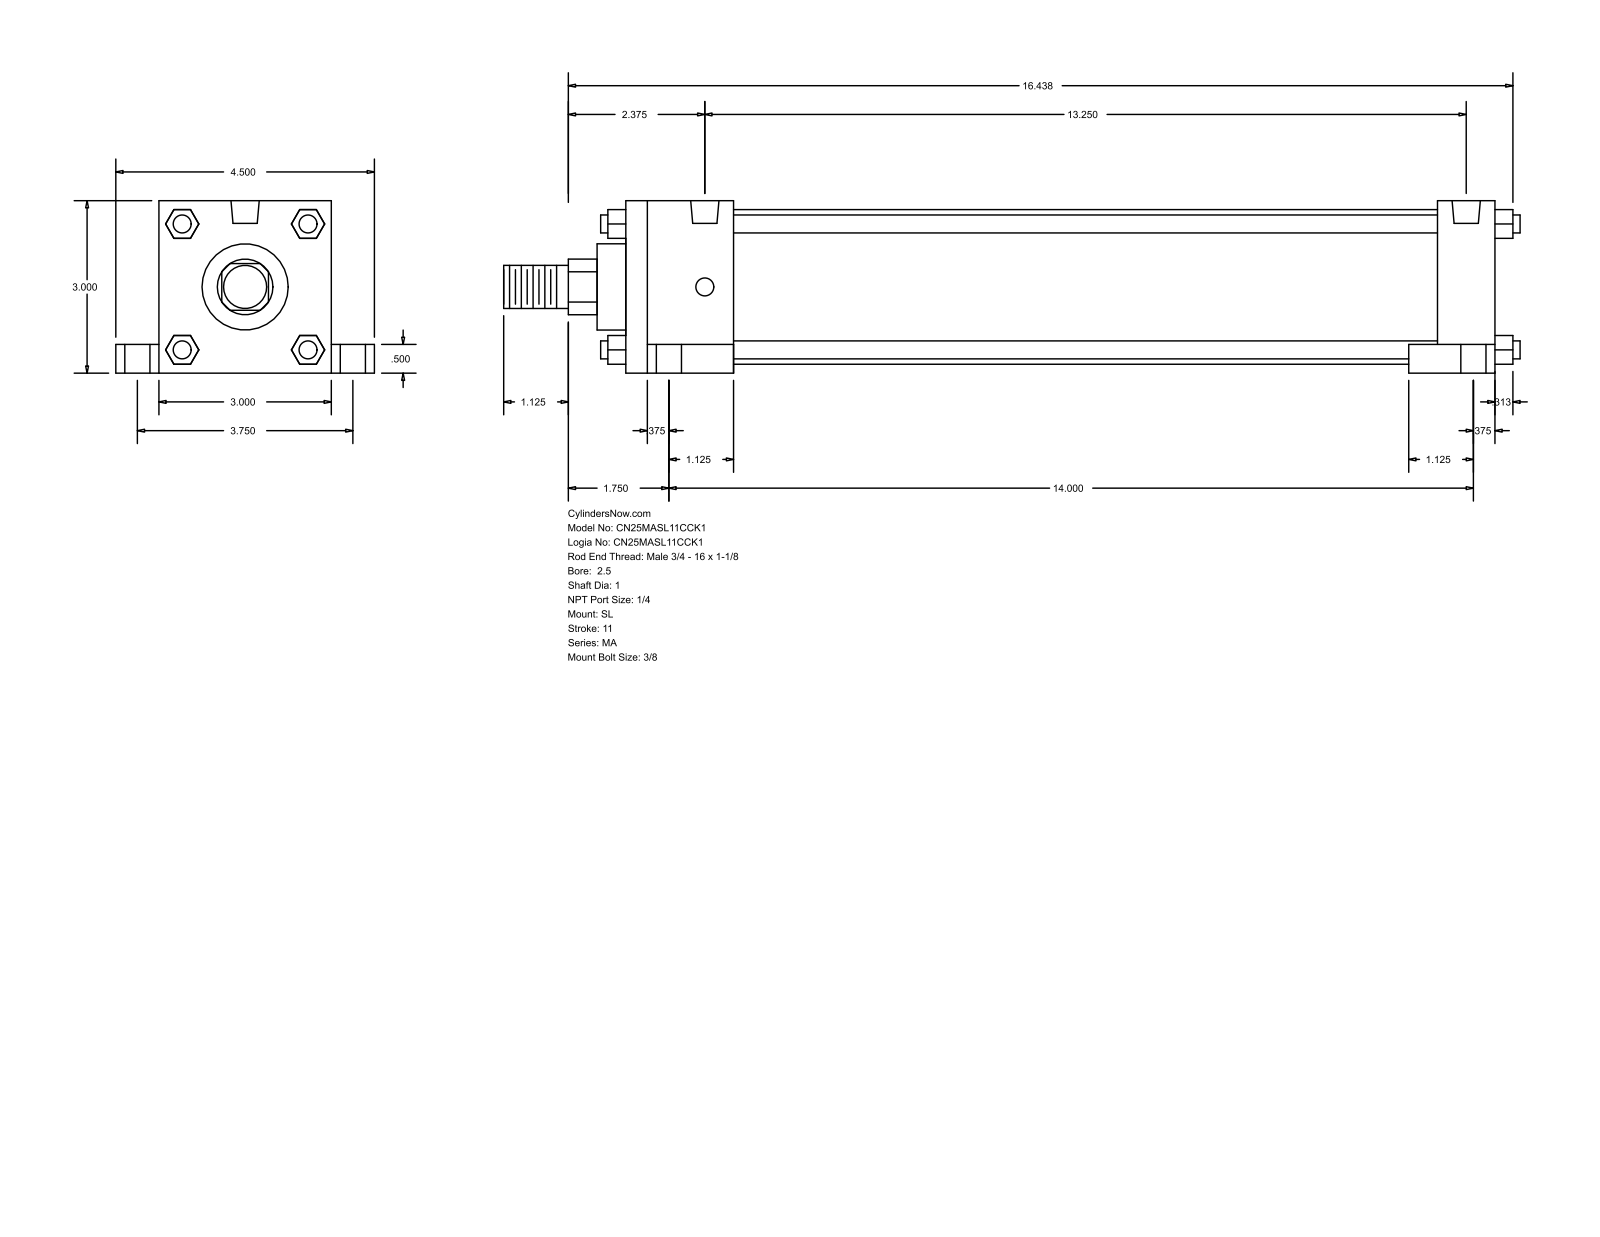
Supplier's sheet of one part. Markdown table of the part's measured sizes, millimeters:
| quantity | value |
| --- | --- |
| part name | MA_SL__0250_1 |
| STEP written by | GSSL Pune (CONFIG_CONTROL_DESIGN) |
| units | millimeters |
| bodies | 0 solids, 148 faces (112 planar, 36 cylindrical, 0 other) |
| overall size | 449.26 × 114.3 × 76.2 |
| round holes (diameter × count) | 7.94 × 4, 11.11 × 4, 17.46 × 4, 12.49 × 2 |
| round bosses / shafts (diameter × count) | 7.94 × 4, 68.33 × 1, 38.1 × 1, 25.4 × 1, 19.05 × 1 |
| partial cylindrical surfaces (radius × count) | 12.29 × 1 |
| main face-to-face distances | 76.2, 384.17, 12.7, 311.15, 25.39, 47.63, 336.54, 358.78, 19.05, 95.25 |
| hole center spacings | 47.73, 50.2, 95.24, 336.55, 343.04, 355.6, 355.63, 368.13 |
